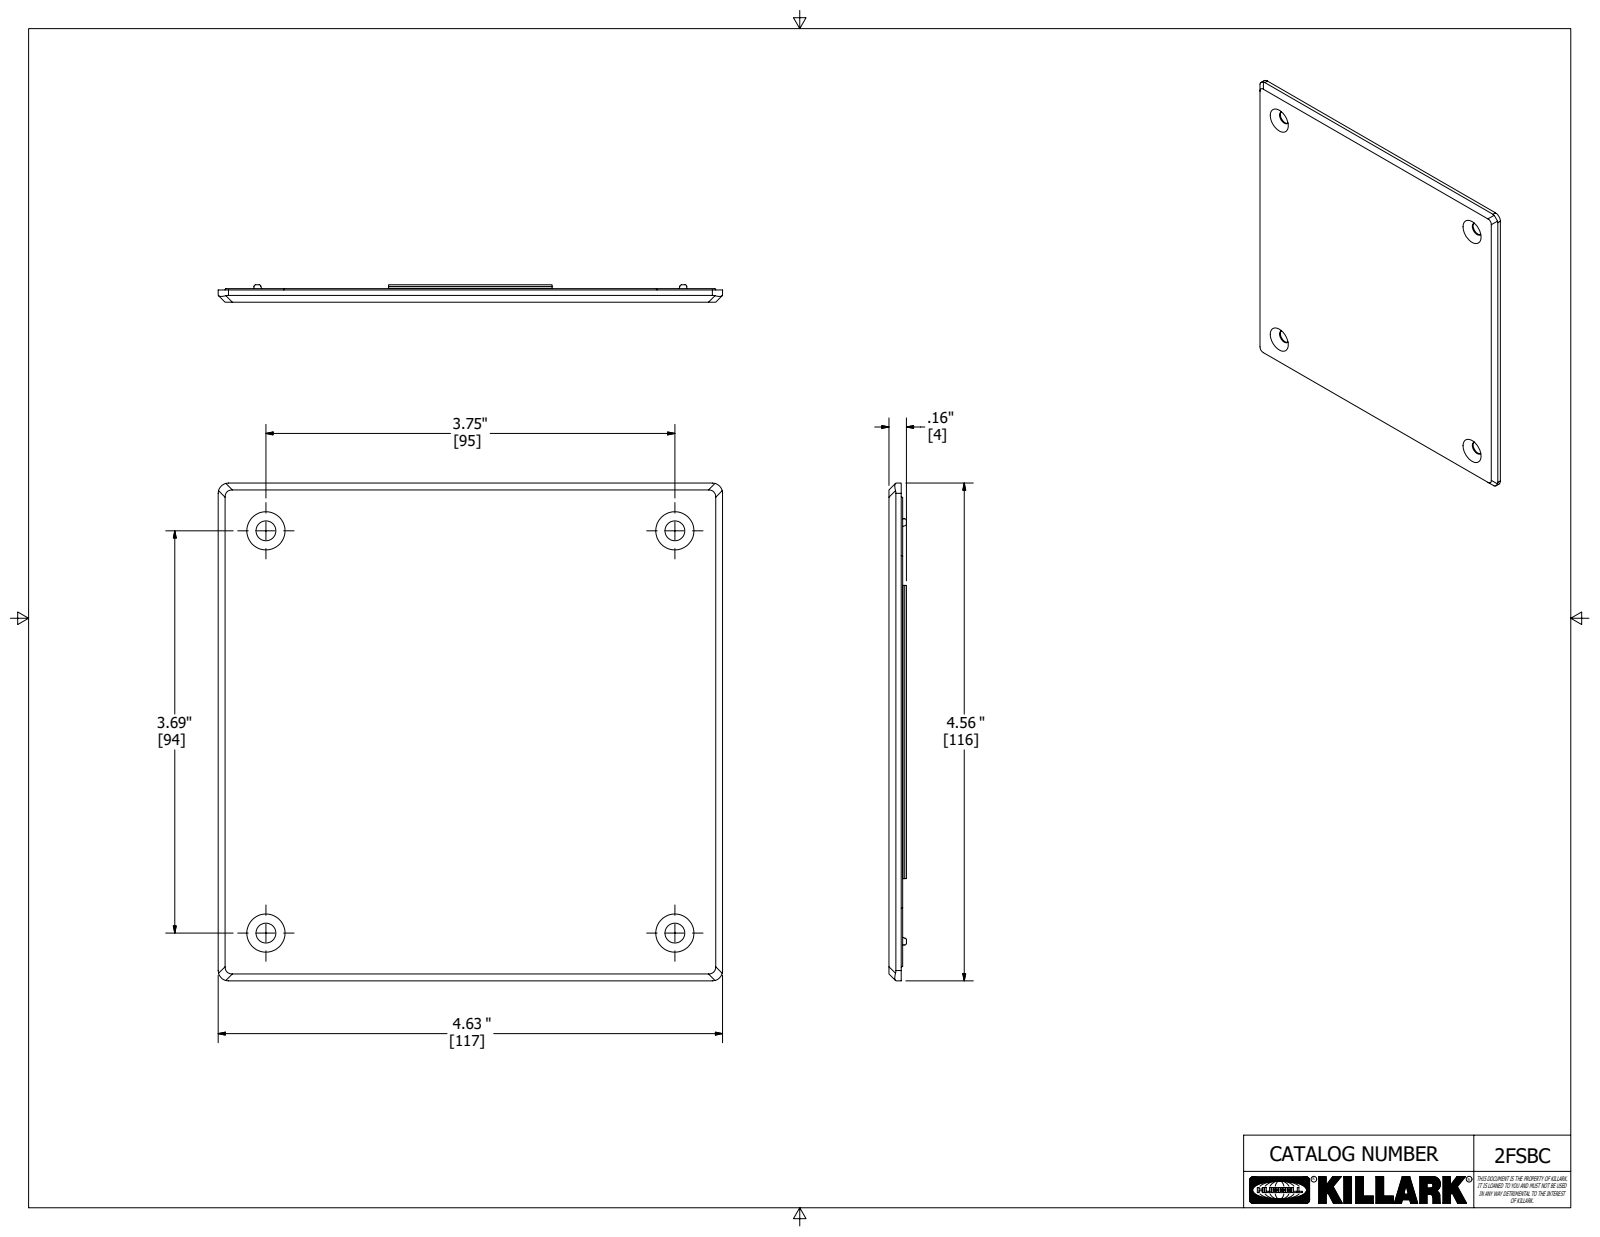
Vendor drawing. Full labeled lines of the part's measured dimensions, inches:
Part name (STEP PRODUCT): 067600B
STEP written by: Autodesk Inventor 2020 (AUTOMOTIVE_DESIGN)
Units: inches
Bodies: 1 solid, 1431 faces (786 planar, 79 cylindrical, 566 other)
Overall size (bounding box): 4.625 × 4.563 × 0.16
Volume: 2.088 in³ · Surface area: 45.04 in²
Round holes (diameter × count): ⌀0.052 ×1, ⌀0.458 ×1
Round bosses / shafts (diameter × count): ⌀0.563 ×1, ⌀0.062 ×1
Partial cylindrical surfaces — rounded edges, fillets, slot ends (radius × count): R0.016 ×12, R0.094 ×8, R0.062 ×6, R0.011 ×2, R0.012 ×2, R0.031 ×2, R0.006 ×1, R0.006 ×1
Main face-to-face distances: 0.094, 0.019, 0.112, 0.015, 0.109, 0.066, 0.047, 0.051, 0.159, 4.562
Hole centre spacings: 0.137
